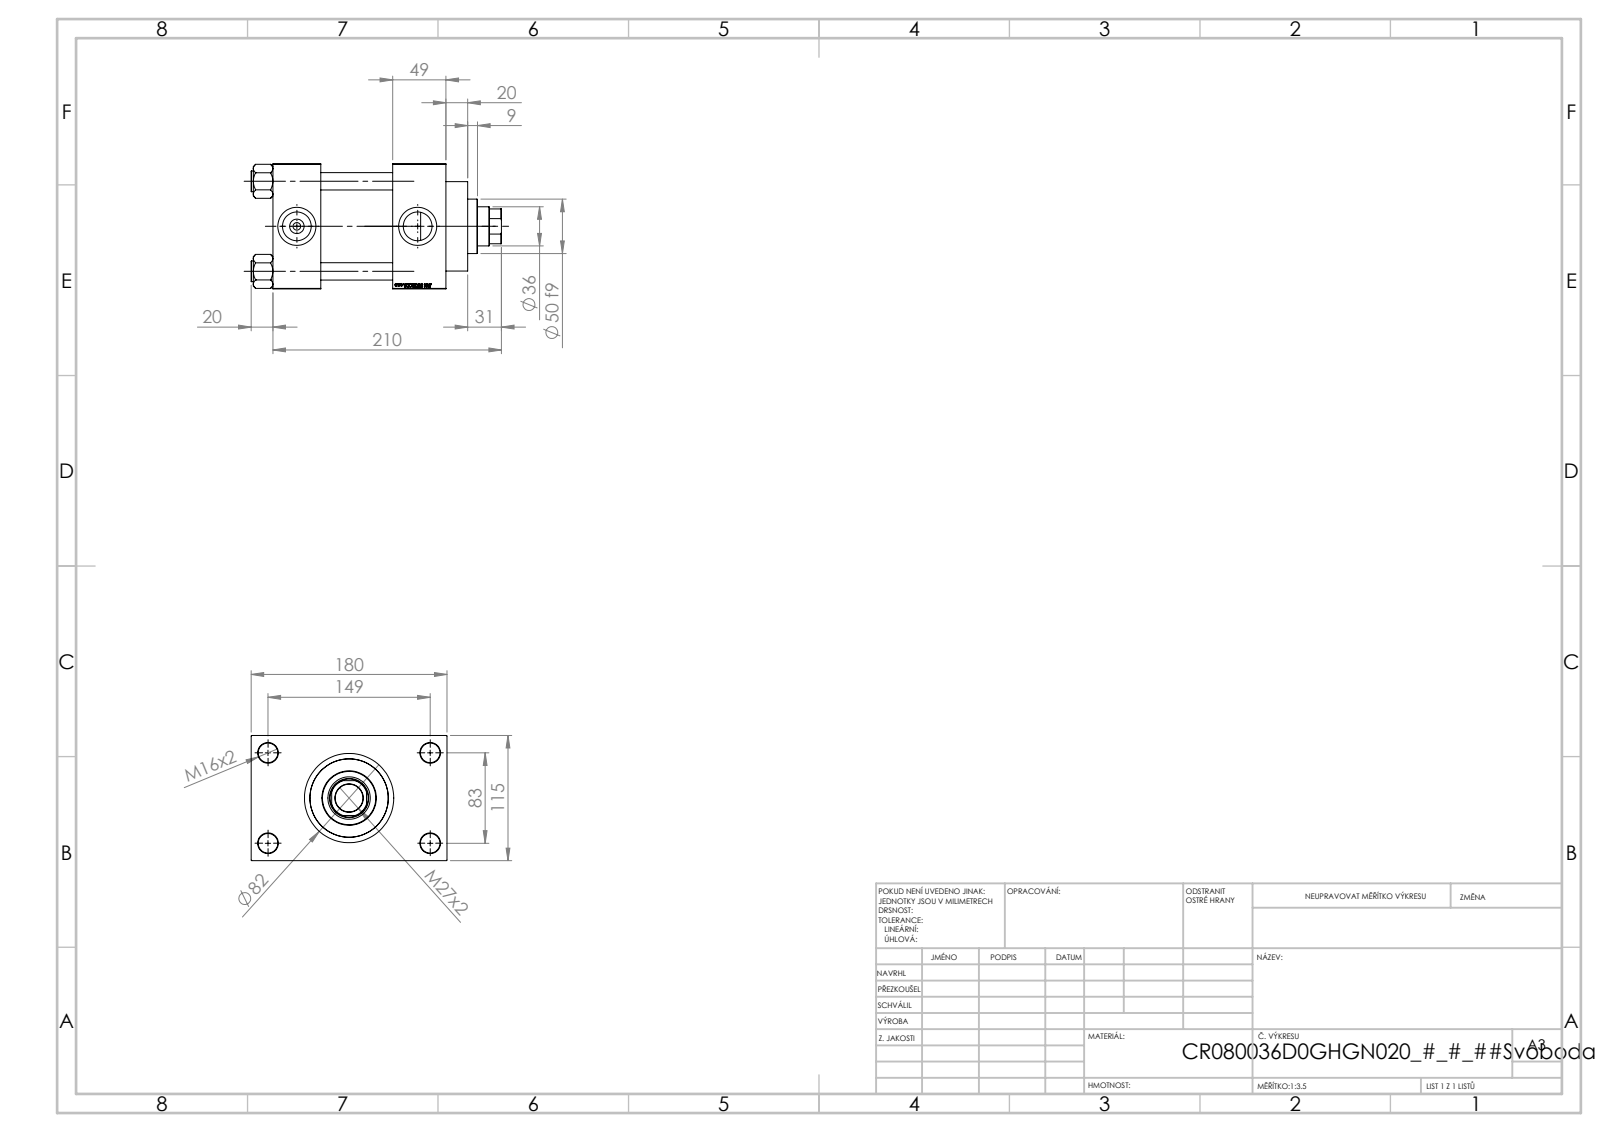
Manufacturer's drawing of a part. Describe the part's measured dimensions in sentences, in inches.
The part is named "V215_VC_A; V215CR_D_Body; NUT_M5_D; V215CR_VCP_D (+1 more)". Its 3-D file was written by "SolidWorks 2019 (CONFIG_CONTROL_DESIGN)". It is 11 solids with 1151 faces: 545 planar, 88 cylindrical and 518 other. Overall it measures 9.055 by 7.087 by 4.528 inches. Its volume is 120.8 cubic inches and its surface area 459.7 square inches. Round holes: 4 of diameter 0.63, 4 of diameter 0.709, 2 of diameter 0.276, 2 of diameter 1.041, 2 of diameter 1.378, 1 of diameter 1.004, 1 of diameter 1.417, 1 of diameter 1.535, 1 of diameter 2.402, 1 of diameter 2.835, 1 of diameter 3.15. Round bosses or shafts: 4 of diameter 0.748, 1 of diameter 3.386, 1 of diameter 3.228, 1 of diameter 1.969. Partial cylindrical surfaces (rounded edges, fillets, slot ends): 1 of radius 0.689. The main face-to-face distances are 4.528, 2.598, 4.331, 1.929, 1.732, 6.26, 1.28, 5.807, 0.787, 2.717. The hole center spacings are 1.305, 2.302, 3.256, 3.357, 3.513, 4.561, 5.607, 3.268.
